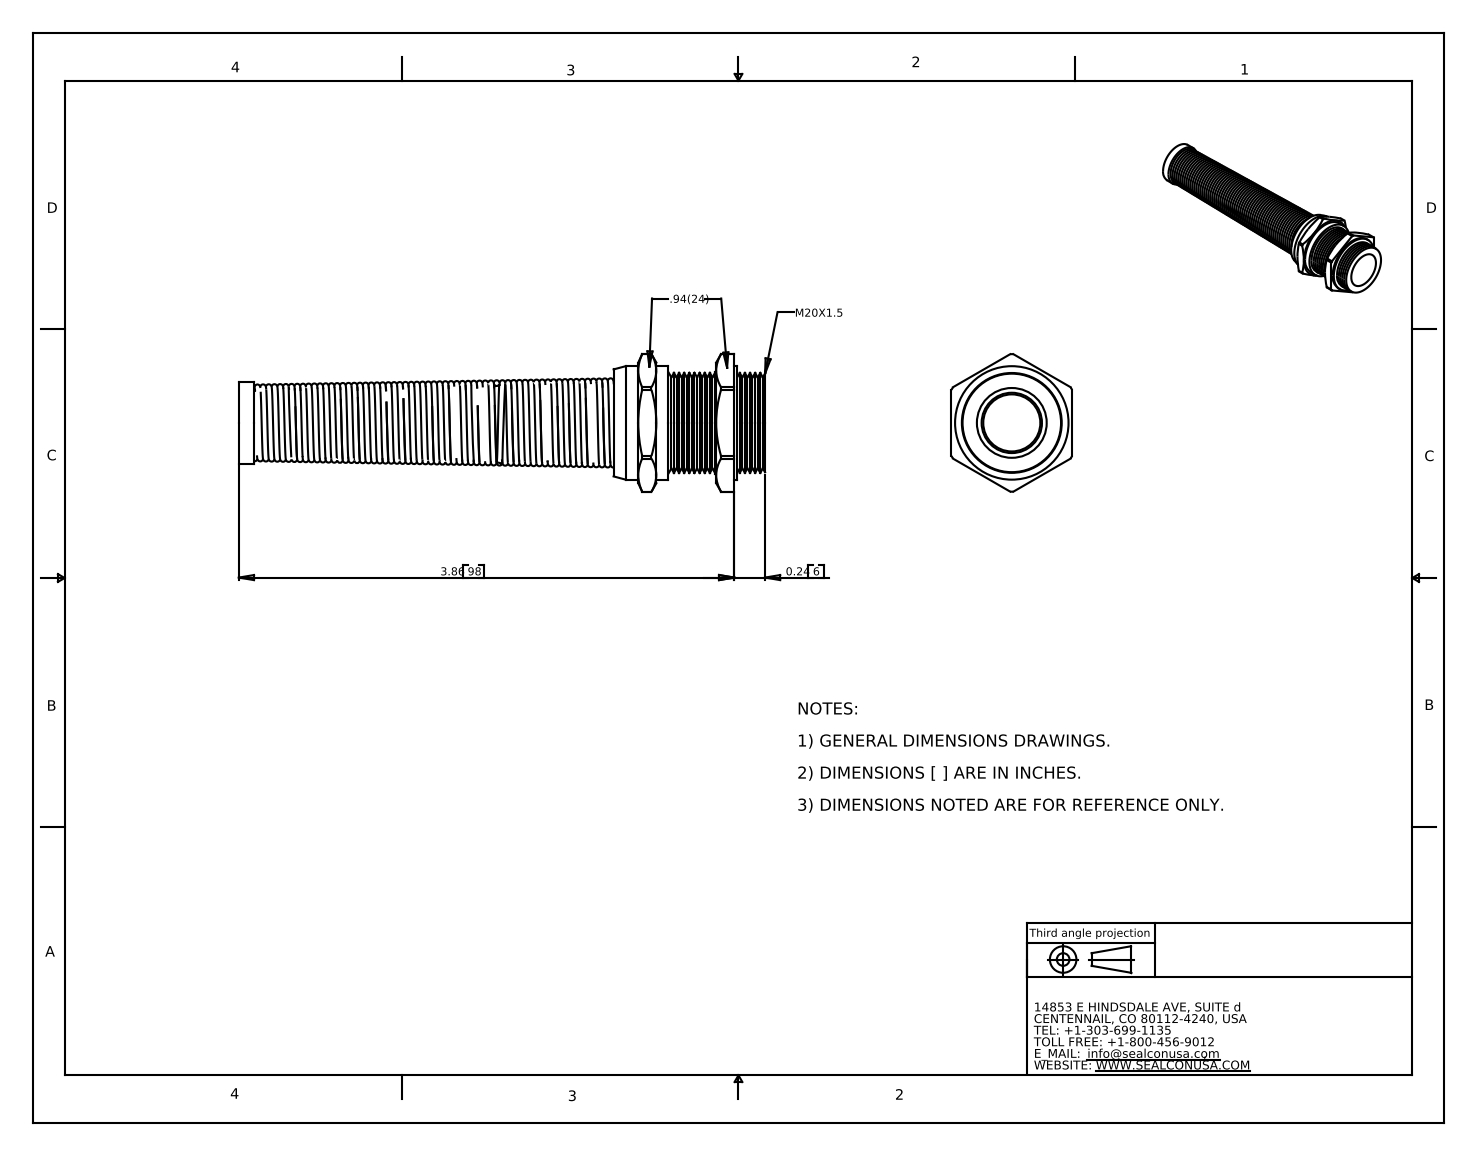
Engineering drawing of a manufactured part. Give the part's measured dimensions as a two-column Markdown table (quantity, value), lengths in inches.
| quantity | value |
| --- | --- |
| part name | CF22MR-BR |
| STEP written by | SolidWorks 2007 (CONFIG_CONTROL_DESIGN) |
| units | inches |
| bodies | 4 solids, 149 faces (29 planar, 34 cylindrical, 86 other) |
| overall size | 4.1 × 1.072 × 0.94 |
| volume | 0.787 in³ |
| surface area | 37.84 in² |
| round holes (diameter × count) | 0.445 × 1, 0.47 × 1, 0.514 × 1, 0.632 × 1 |
| round bosses / shafts (diameter × count) | 0.884 × 1, 0.79 × 1, 0.639 × 1 |
| partial cylindrical surfaces (radius × count) | 0.536 × 1 |
| main face-to-face distances | 0.94, 0.607, 0.192, 0.141, 1.18, 0.988, 0.965, 0.773, 0.215, 0.799 |
